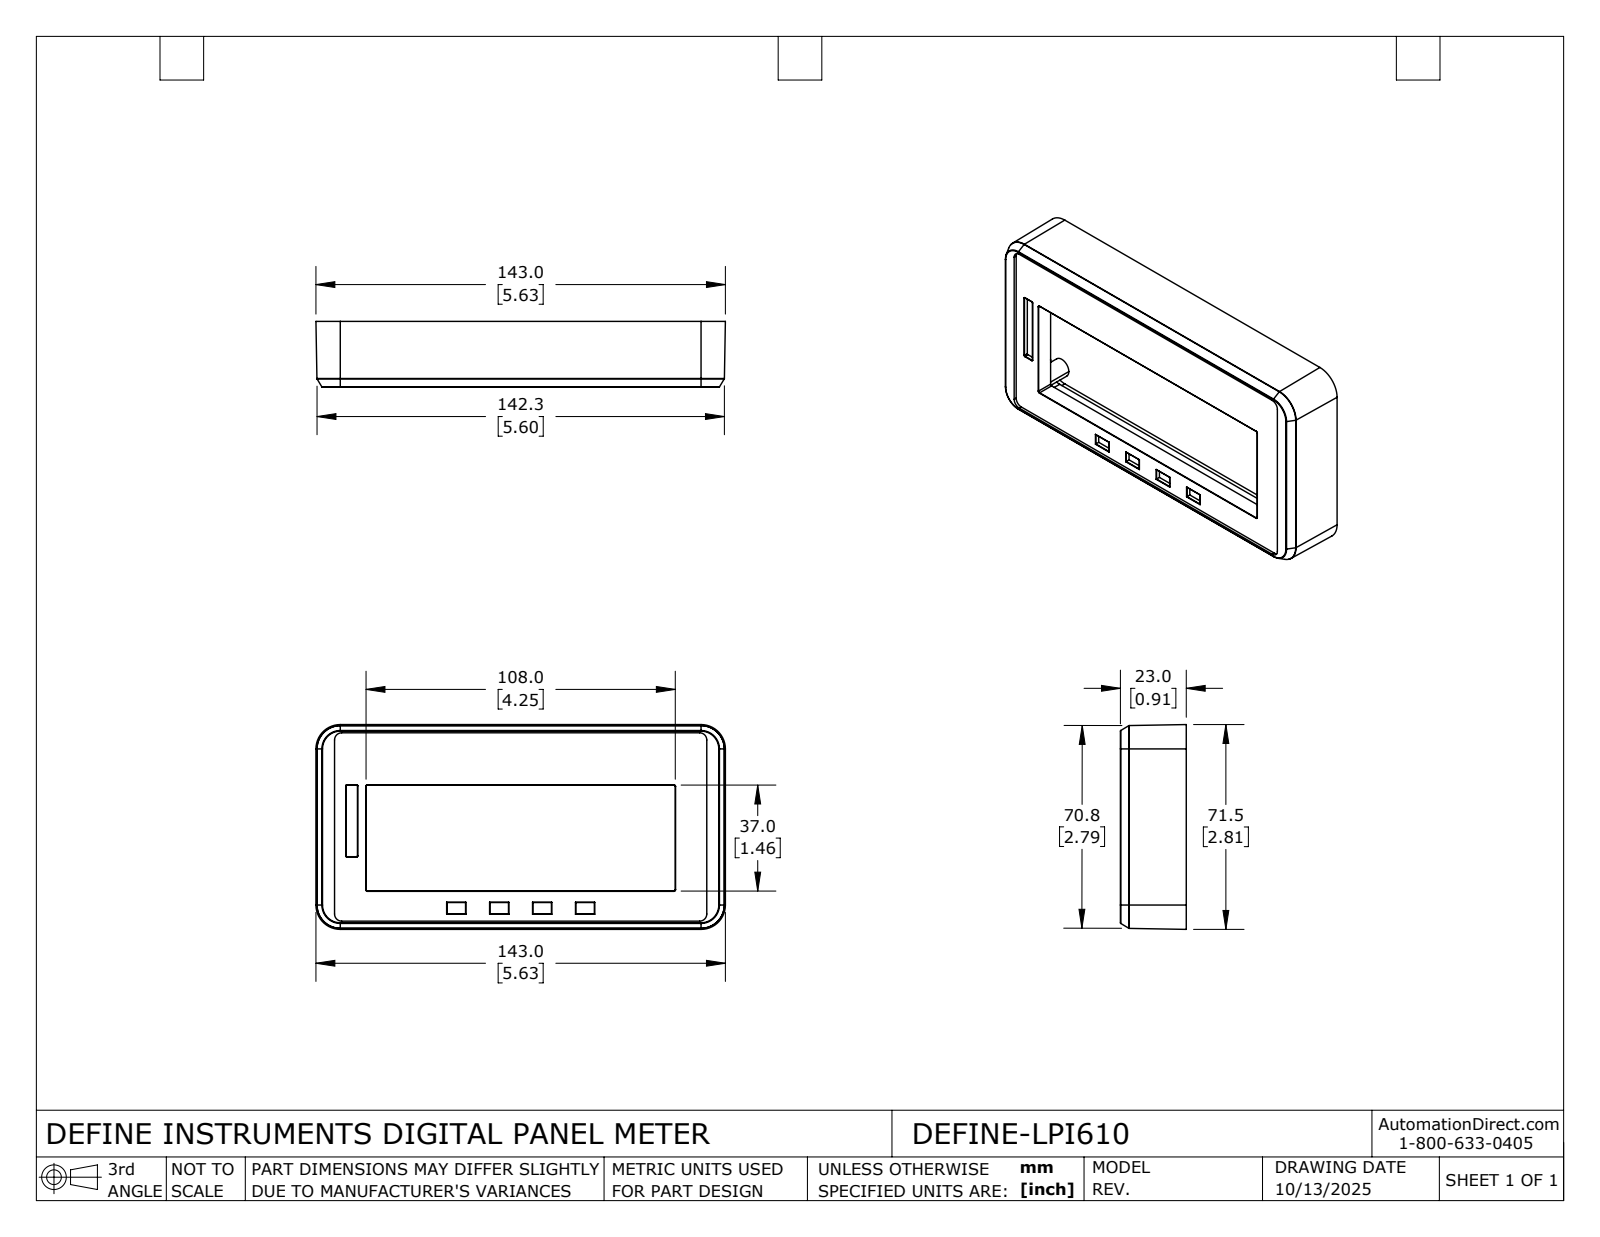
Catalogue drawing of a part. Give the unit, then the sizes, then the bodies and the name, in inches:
Units: inches
Overall size (bounding box): 5.63 × 2.815 × 0.906
Round holes (diameter × count): ⌀0.138 ×4
Round bosses / shafts (diameter × count): ⌀0.276 ×4
Partial cylindrical surfaces — rounded edges, fillets, slot ends (radius × count): R0.004 ×17, R0.01 ×12, R0.02 ×4, R0.079 ×4, R0.098 ×4, R0.276 ×4
Main face-to-face distances: 0.098, 0.059, 0.807, 0.63, 0.039, 1.457, 0.866, 0.906, 0.709, 0.768
Hole centre spacings: 2.017, 5.097, 4.488, 4.882
Volume: 2.019 in³ · Surface area: 53.63 in²
Bodies: 1 solid, 206 faces (66 planar, 108 cylindrical, 32 other)
Part name (STEP PRODUCT): DEFINE-LPI610
STEP written by: SolidWorks 2024 (AUTOMOTIVE_DESIGN)
